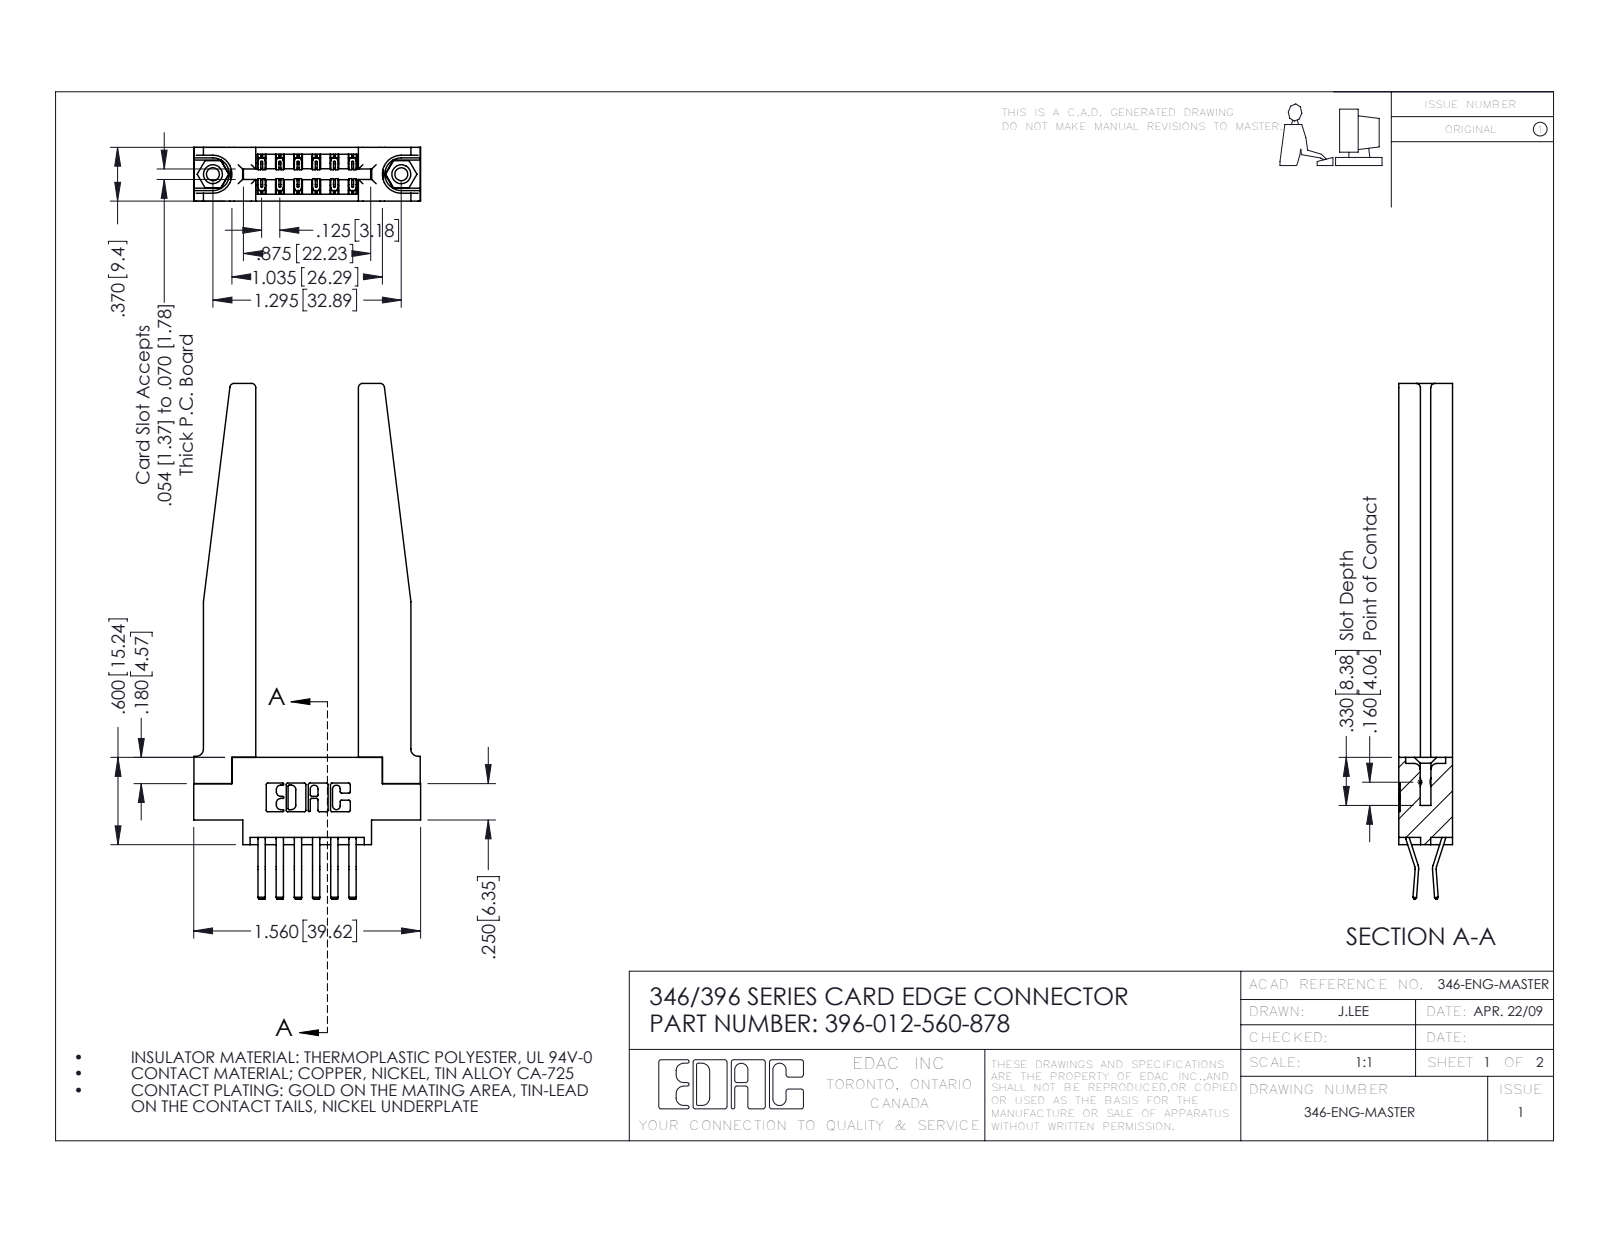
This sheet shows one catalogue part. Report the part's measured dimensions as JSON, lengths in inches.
{"part_name": "396-012-560-878; 346-220-078_345-220-078; 345-250-001_345-250-001-102; 345-292-001_560 Tail (+1 more)", "step_written_by": "SolidWorks 2016 (CONFIG_CONTROL_DESIGN)", "units": "inches", "bodies": {"solids": 17, "faces": 1008, "planar": 642, "cylindrical": 314, "other": 52}, "overall_size": [3.545, 1.56, 0.37], "volume_in3": 0.636, "surface_area_in2": 17.33, "round_holes": [[0.089, 2], [0.125, 2], [0.156, 2], [0.064, 1]], "round_bosses_or_shafts": [[0.155, 2]], "partial_cylinders_radius": [[0.01, 22], [0.006, 18], [0.03, 8], [0.007, 6], [0.031, 6], [0.05, 4], [0.026, 3], [0.01, 2]], "face_to_face_distances": [0.37, 0.15, 0.22, 0.25, 0.706, 0.072, 0.148, 0.102, 0.048, 0.322], "hole_center_spacings": [0.246, 1.092, 1.295]}
